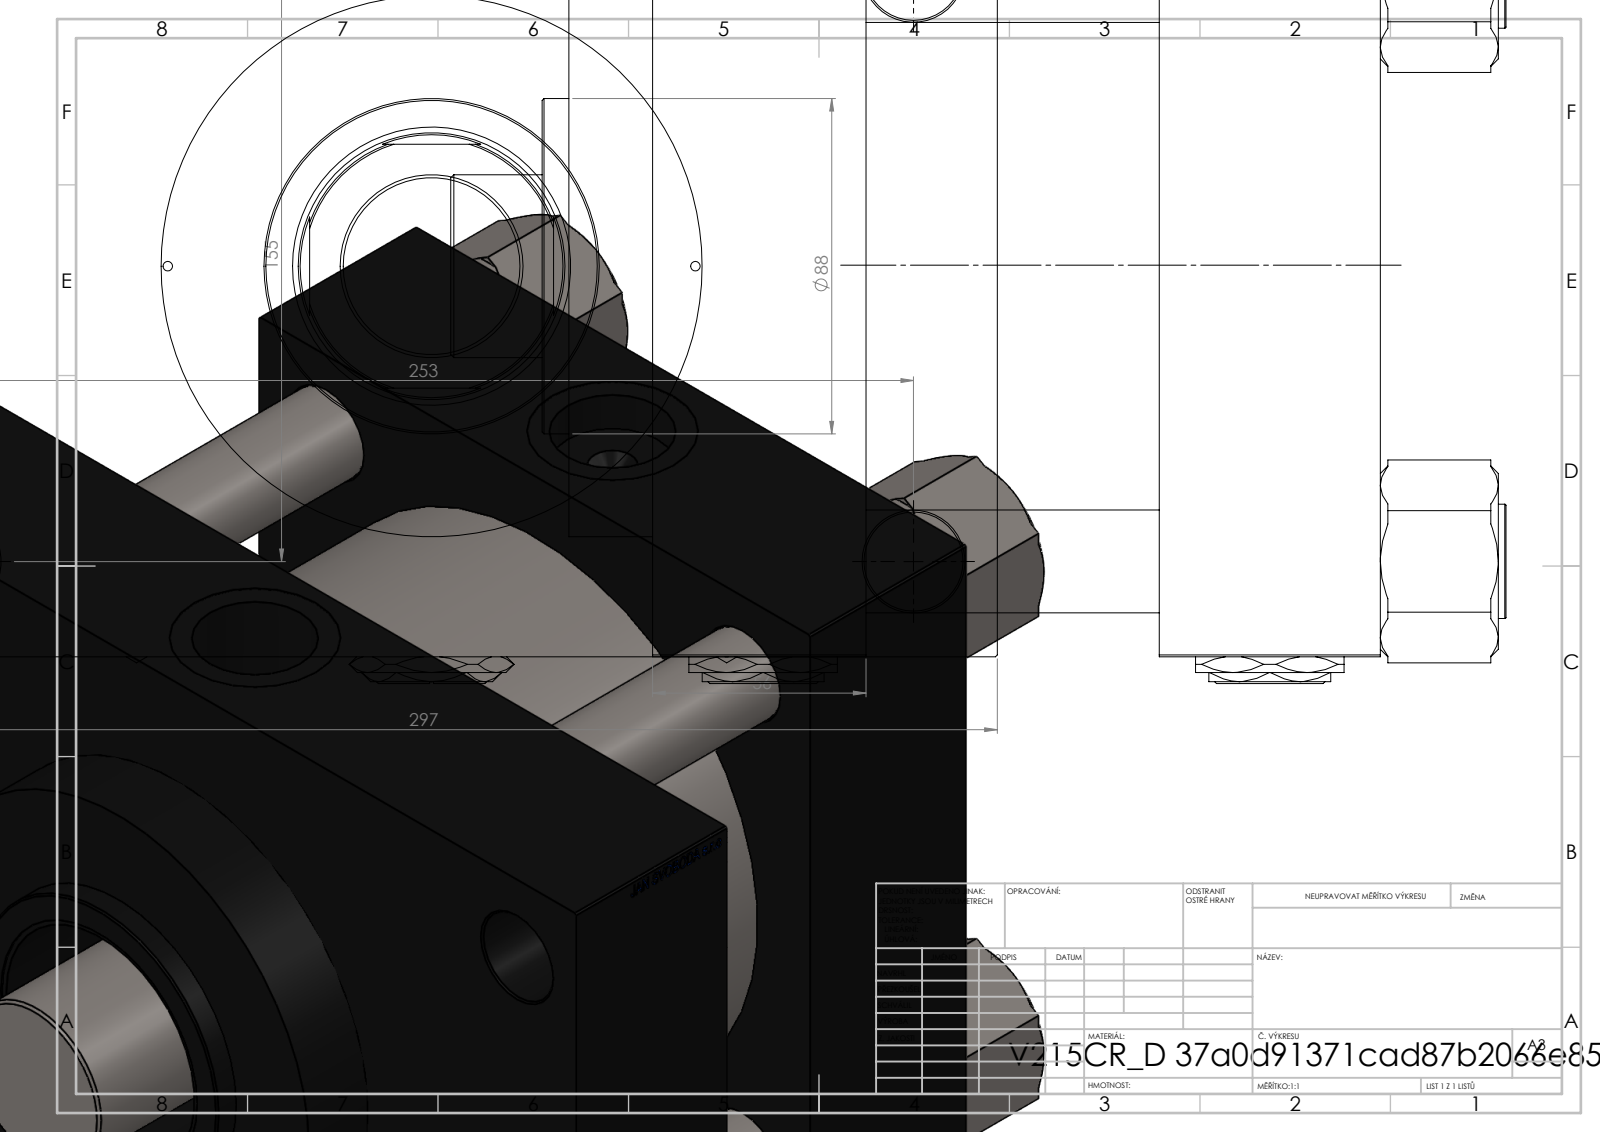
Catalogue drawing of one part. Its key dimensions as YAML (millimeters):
part_name: "V215CR_VCP_D; ROD_END_AH; NUT_M5_D; V215_VC_A (+3 more)"
step_written_by: "SolidWorks 2019 (CONFIG_CONTROL_DESIGN)"
units: millimeters
bodies: {solids: 14, faces: 1270, planar: 598, cylindrical: 106, other: 566}
overall_size: [297, 277, 213.57]
volume: 6872000
surface_area: 698883
round_holes:
  - {diameter: 26, count: 4}
  - {diameter: 27, count: 4}
  - {diameter: 2.5, count: 2}
  - {diameter: 7, count: 2}
  - {diameter: 33.24, count: 2}
  - {diameter: 45, count: 2}
  - {diameter: 46.5, count: 1}
  - {diameter: 70, count: 1}
  - {diameter: 73, count: 1}
  - {diameter: 120, count: 1}
  - {diameter: 142, count: 1}
  - {diameter: 160, count: 1}
round_bosses_or_shafts:
  - {diameter: 30, count: 4}
  - {diameter: 166, count: 1}
  - {diameter: 88, count: 1}
  - {diameter: 48, count: 1}
  - {diameter: 46, count: 1}
partial_cylinders:
  - {radius: 34, count: 1}
face_to_face_distances: [135, 58, 77, 133, 191, 56, 205, 46, 251, 85]
hole_center_spacings: [49.05, 77.88, 96.35, 109.53, 148.35, 154.9, 162.53, 165.89]
